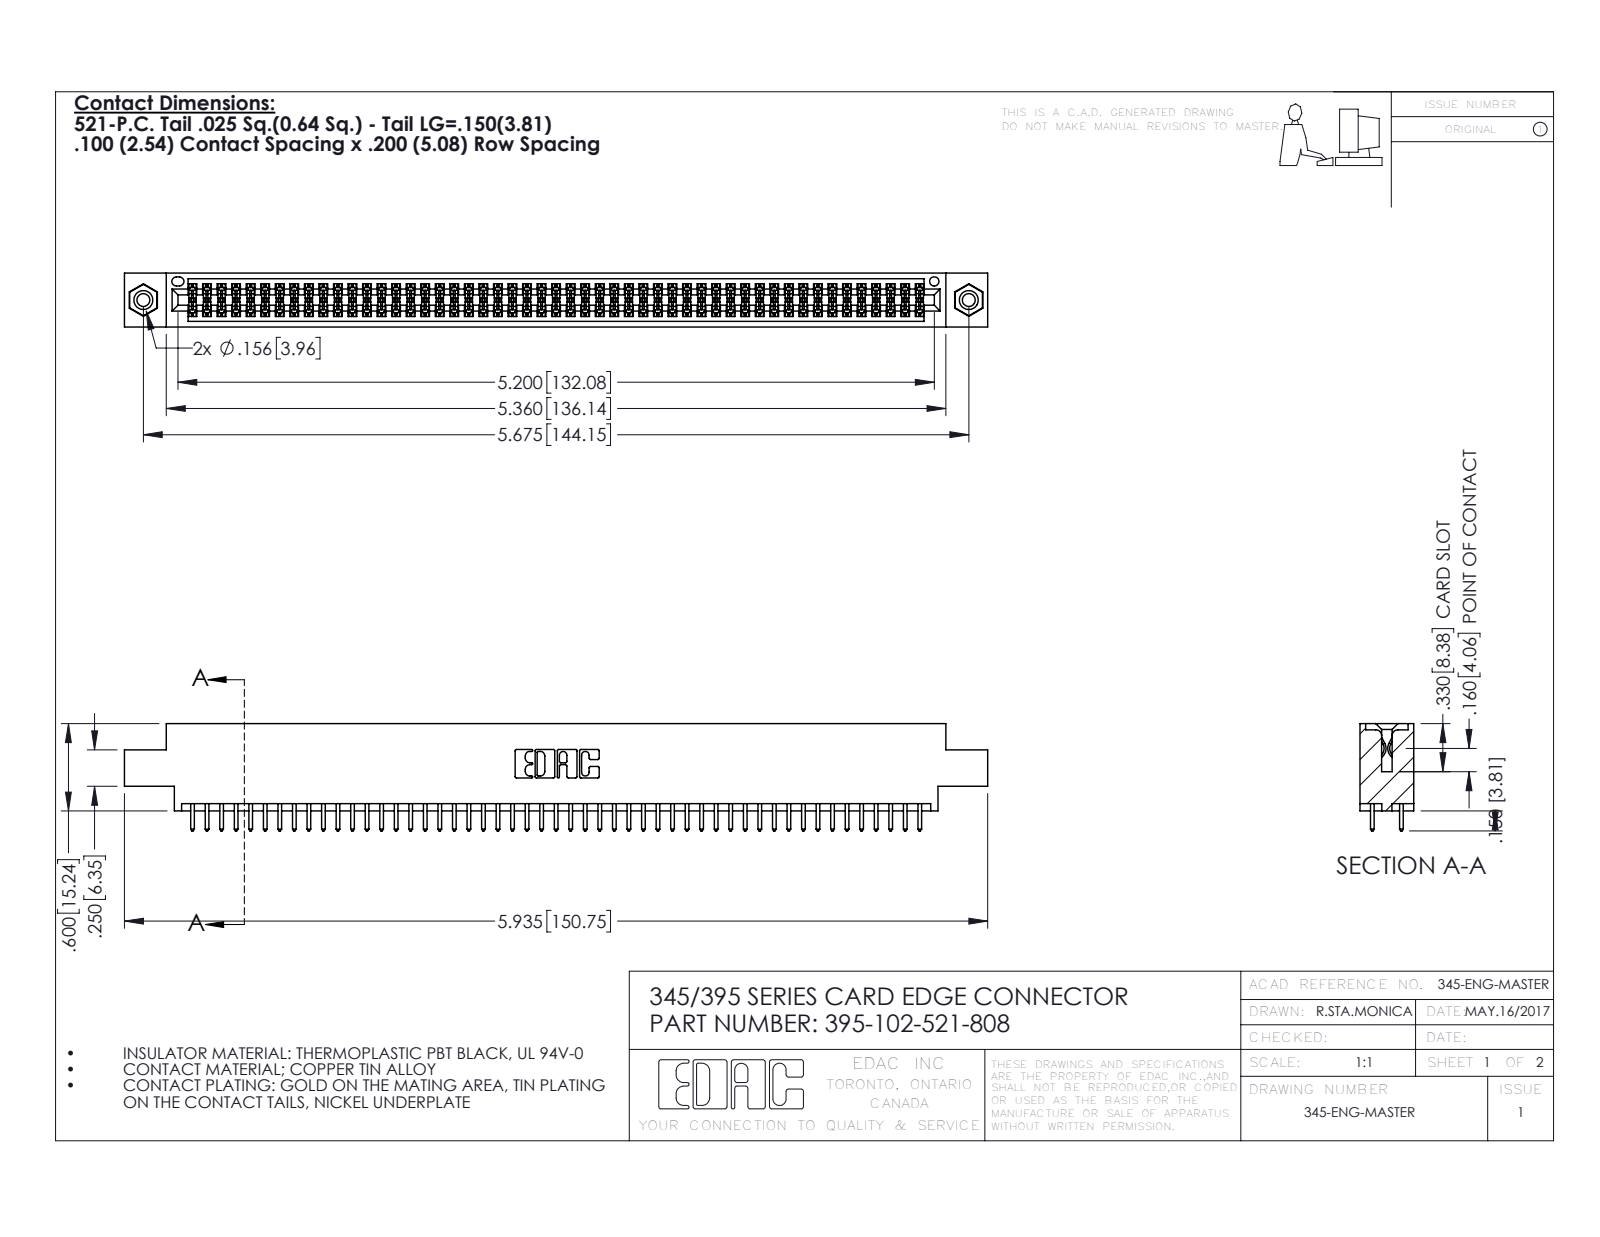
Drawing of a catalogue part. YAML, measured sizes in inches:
part_name: "345-250-001_345-250-003-102; 395-102-521-808; 345-292-001_345-293-121; 345 Part_0.170 Offset - 0.156 Dia-TI"
step_written_by: "SolidWorks 2016 (CONFIG_CONTROL_DESIGN)"
units: inches
bodies: {solids: 105, faces: 5290, planar: 3482, cylindrical: 1792, other: 16}
overall_size: [5.935, 0.737, 0.37]
volume: 0.889
surface_area: 33.47
round_holes:
  - {diameter: 0.089, count: 2}
  - {diameter: 0.125, count: 2}
  - {diameter: 0.156, count: 2}
  - {diameter: 0.064, count: 1}
round_bosses_or_shafts:
  - {diameter: 0.155, count: 2}
partial_cylinders:
  - {radius: 0.006, count: 153}
  - {radius: 0.01, count: 102}
  - {radius: 0.01, count: 22}
  - {radius: 0.007, count: 6}
  - {radius: 0.031, count: 6}
  - {radius: 0.026, count: 3}
  - {radius: 0.014, count: 2}
  - {radius: 0.019, count: 2}
face_to_face_distances: [0.072, 0.298, 0.2, 0.37, 0.098, 0.272, 0.025, 0.225, 0.175, 0.149]
hole_center_spacings: [0.27, 5.439, 5.675]
